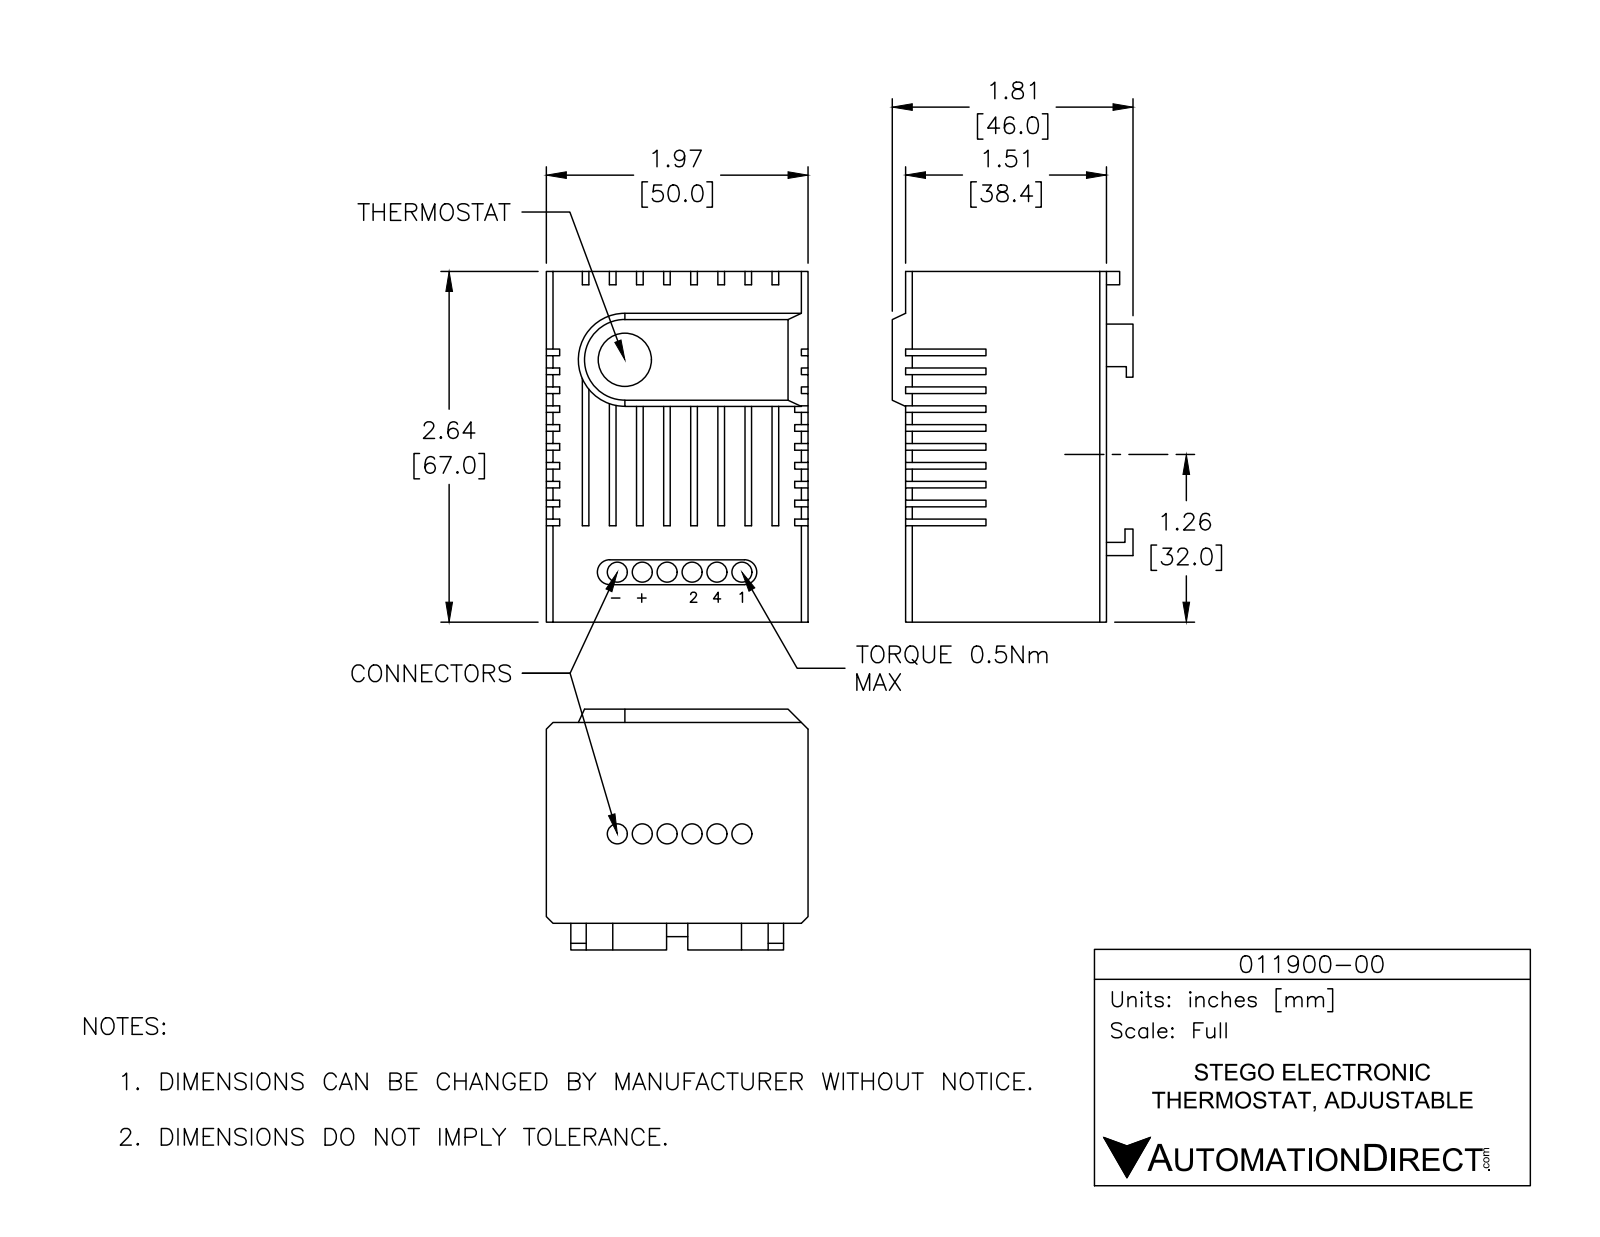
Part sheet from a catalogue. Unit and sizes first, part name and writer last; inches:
Units: inches
Overall size (bounding box): 2.638 × 1.969 × 1.811
Round holes (diameter × count): ⌀0.15 ×12, ⌀0.4 ×1
Partial cylindrical surfaces — rounded edges, fillets, slot ends (radius × count): R0.094 ×2
Main face-to-face distances: 1.969, 1.511, 2.638, 0.05, 0.1, 0.204, 0.408, 0.142, 0.612, 1.611
Hole centre spacings: 0.187, 0.563, 0.375, 0.375, 0.75, 0.188, 0.937, 1.599
Volume: 7.818 in³ · Surface area: 31.85 in²
Bodies: 1 solid, 275 faces (246 planar, 28 cylindrical, 1 other)
Part name (STEP PRODUCT): PRODUCT_NAME_1
STEP written by: ACIS (AUTOMOTIVE_DESIGN_CC2)
